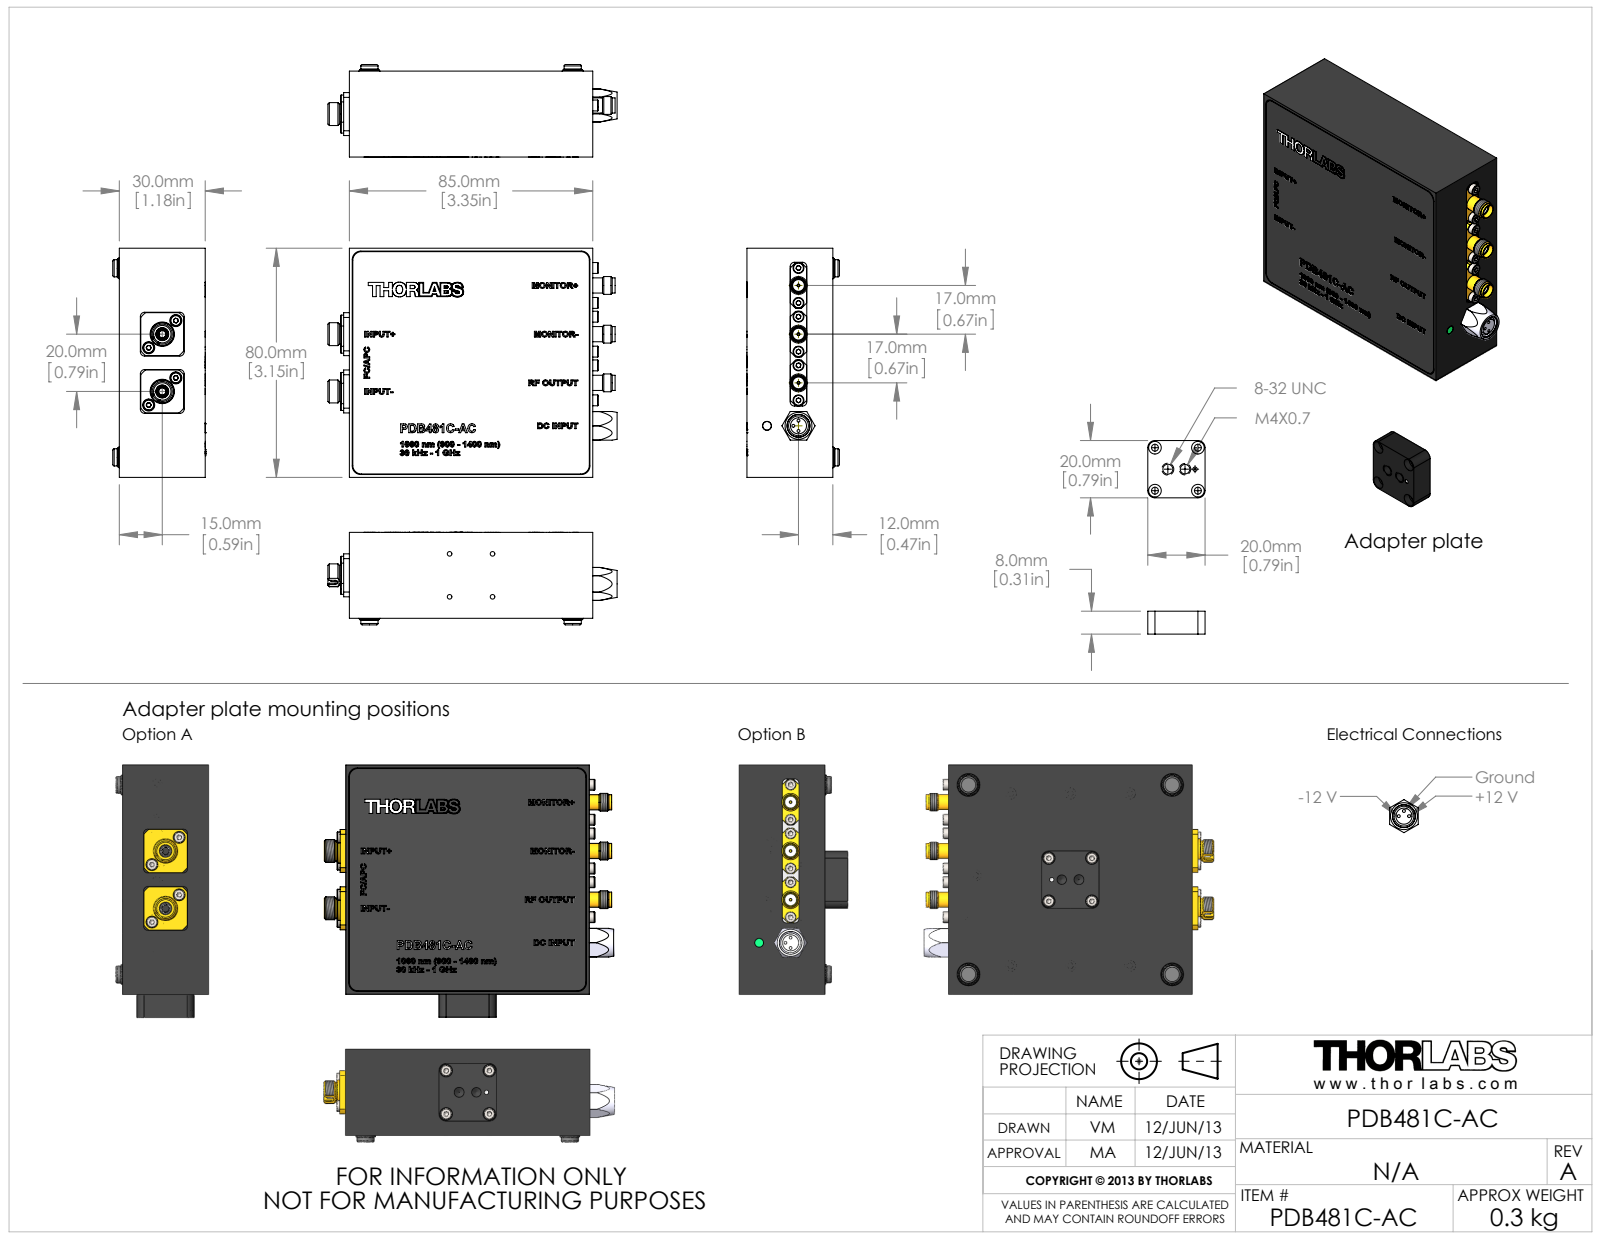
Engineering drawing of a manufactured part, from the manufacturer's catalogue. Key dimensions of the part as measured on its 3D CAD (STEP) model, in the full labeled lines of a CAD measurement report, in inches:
Part name (STEP PRODUCT): Socket Head Cap Screw_DIN_DIN 912 M2 x 3 --- 3N; M0092-0699 Grundkörper PDB480C-AC Rev C; M0075-02-0032 SMABuchse (Rosenberger 32K722-500E3); M0075-22-0001 PDA10Bx (RKMF) (+8 more)
STEP written by: SolidWorks 2012 (AUTOMOTIVE_DESIGN)
Units: inches
Bodies: 84 solids, 3137 faces (1803 planar, 542 cylindrical, 792 other)
Overall size (bounding box): 3.976 × 3.465 × 1.496
Volume: 5.438 in³ · Surface area: 90.06 in²
Round holes (diameter × count): ⌀0.063 ×29, ⌀0.094 ×8, ⌀0.173 ×8, ⌀0.315 ×7, ⌀0.102 ×6, ⌀0.059 ×4, ⌀0.031 ×3, ⌀0.039 ×3, ⌀0.161 ×3, ⌀0.165 ×3, ⌀0.185 ×3, ⌀0.126 ×2
Round bosses / shafts (diameter × count): ⌀0.15 ×25, ⌀0.079 ×25, ⌀0.165 ×8, ⌀0.091 ×8, ⌀0.236 ×6, ⌀0.062 ×4, ⌀0.245 ×3, ⌀0.209 ×3
Partial cylindrical surfaces — rounded edges, fillets, slot ends (radius × count): R0.059 ×12, R0.118 ×12, R0.197 ×10, R0.098 ×8, R0.04 ×4, R0.315 ×3, R0.374 ×2, R0.226 ×1
Main face-to-face distances: 1.181, 1.169, 0.236, 0.933, 0.945, 0.217, 3.15, 3.346, 0.079, 2.933
Hole centre spacings: 0.591, 0.344, 0.508, 0.24, 0.669, 0.111, 0.298, 0.429
